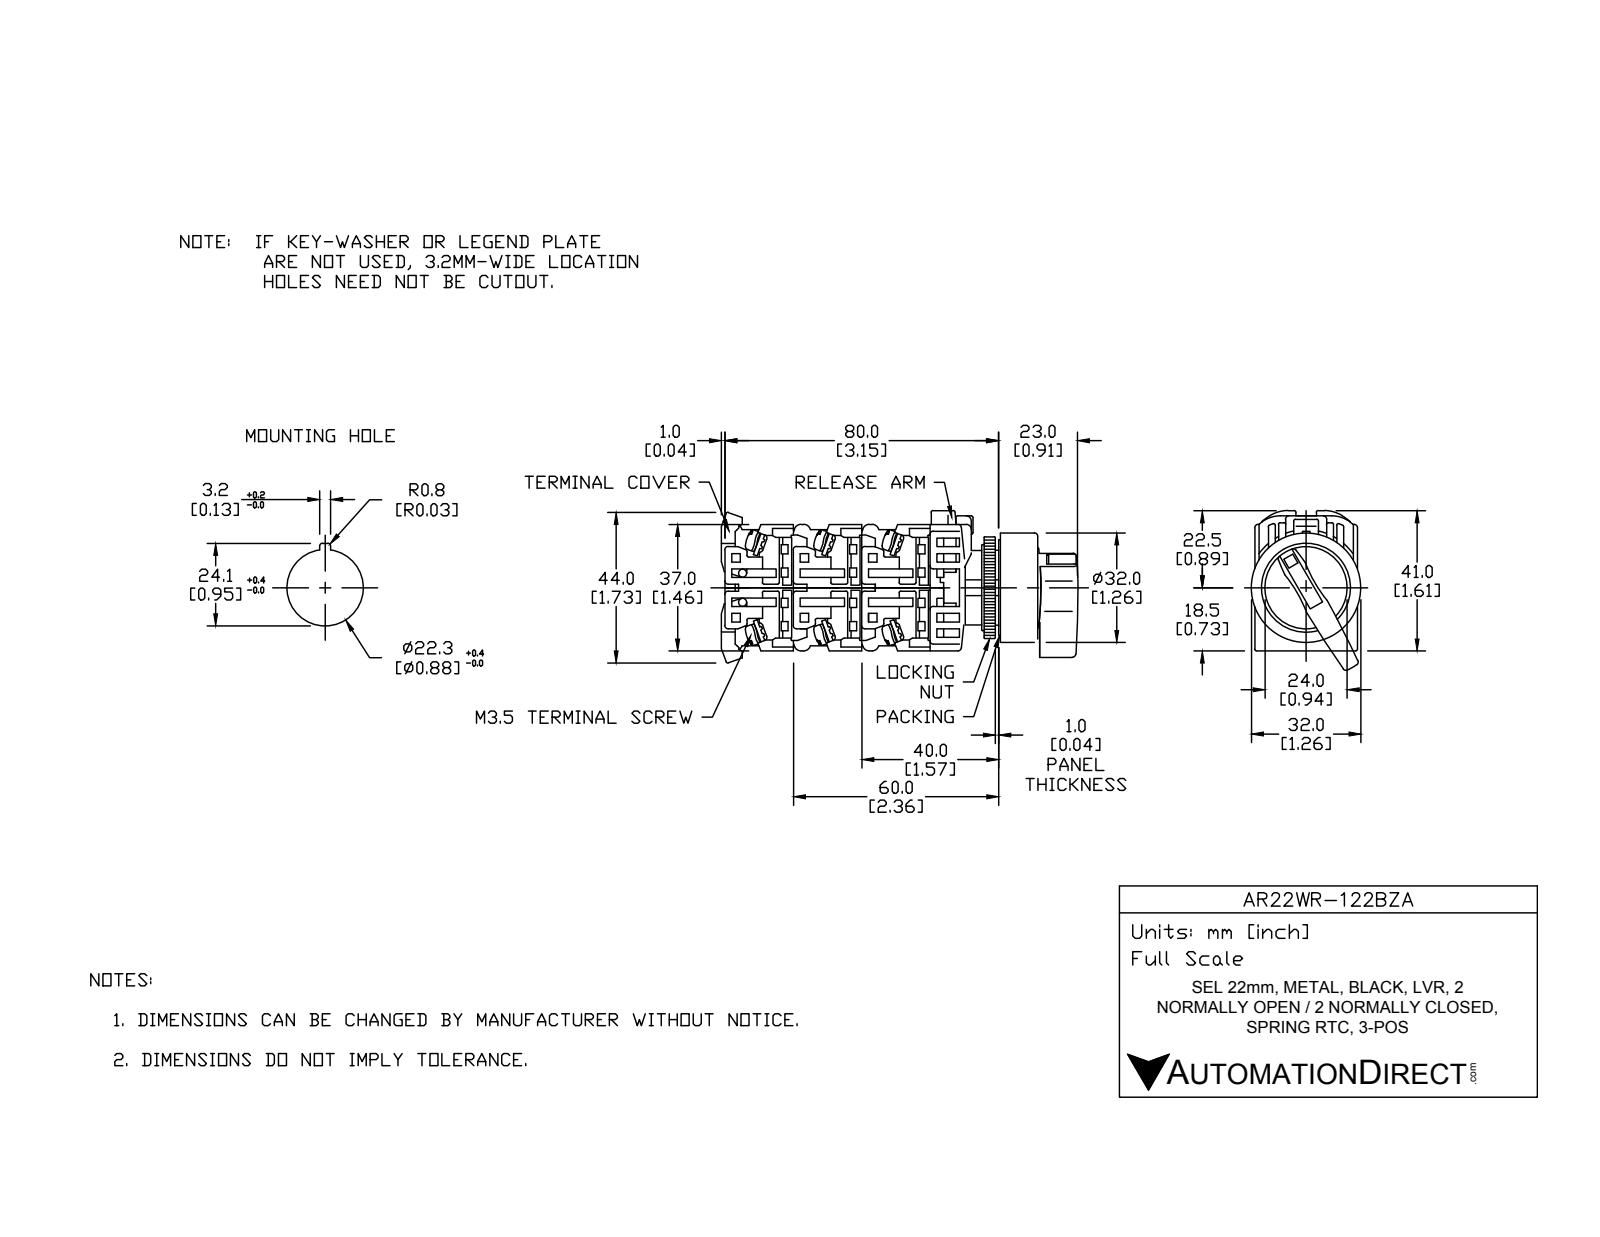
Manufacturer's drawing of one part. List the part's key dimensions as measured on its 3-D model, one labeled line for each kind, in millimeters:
Part name (STEP PRODUCT): AR22WR-122BZA
STEP written by: SolidWorks 2017 (AUTOMOTIVE_DESIGN)
Units: millimetres
Bodies: 18 solids, 467 faces (318 planar, 121 cylindrical, 28 other)
Overall size (bounding box): 64 × 50 × 32
Volume: 39 304 mm³ · Surface area: 25 226 mm²
Round holes (diameter × count): ⌀21.8 ×1, ⌀22 ×1, ⌀25 ×1, ⌀31 ×1
Round bosses / shafts (diameter × count): ⌀5 ×4, ⌀32 ×1, ⌀30.5 ×1, ⌀29.8 ×1, ⌀24 ×1, ⌀21.75 ×1, ⌀17 ×1
Partial cylindrical surfaces — rounded edges, fillets, slot ends (radius × count): R0.5 ×39, R1 ×10, R1.75 ×8, R5 ×4, R4 ×2, R16.59 ×1, R17.59 ×1
Main face-to-face distances: 1, 18, 3, 28.5, 20, 48.5, 29, 0.5, 10, 21
